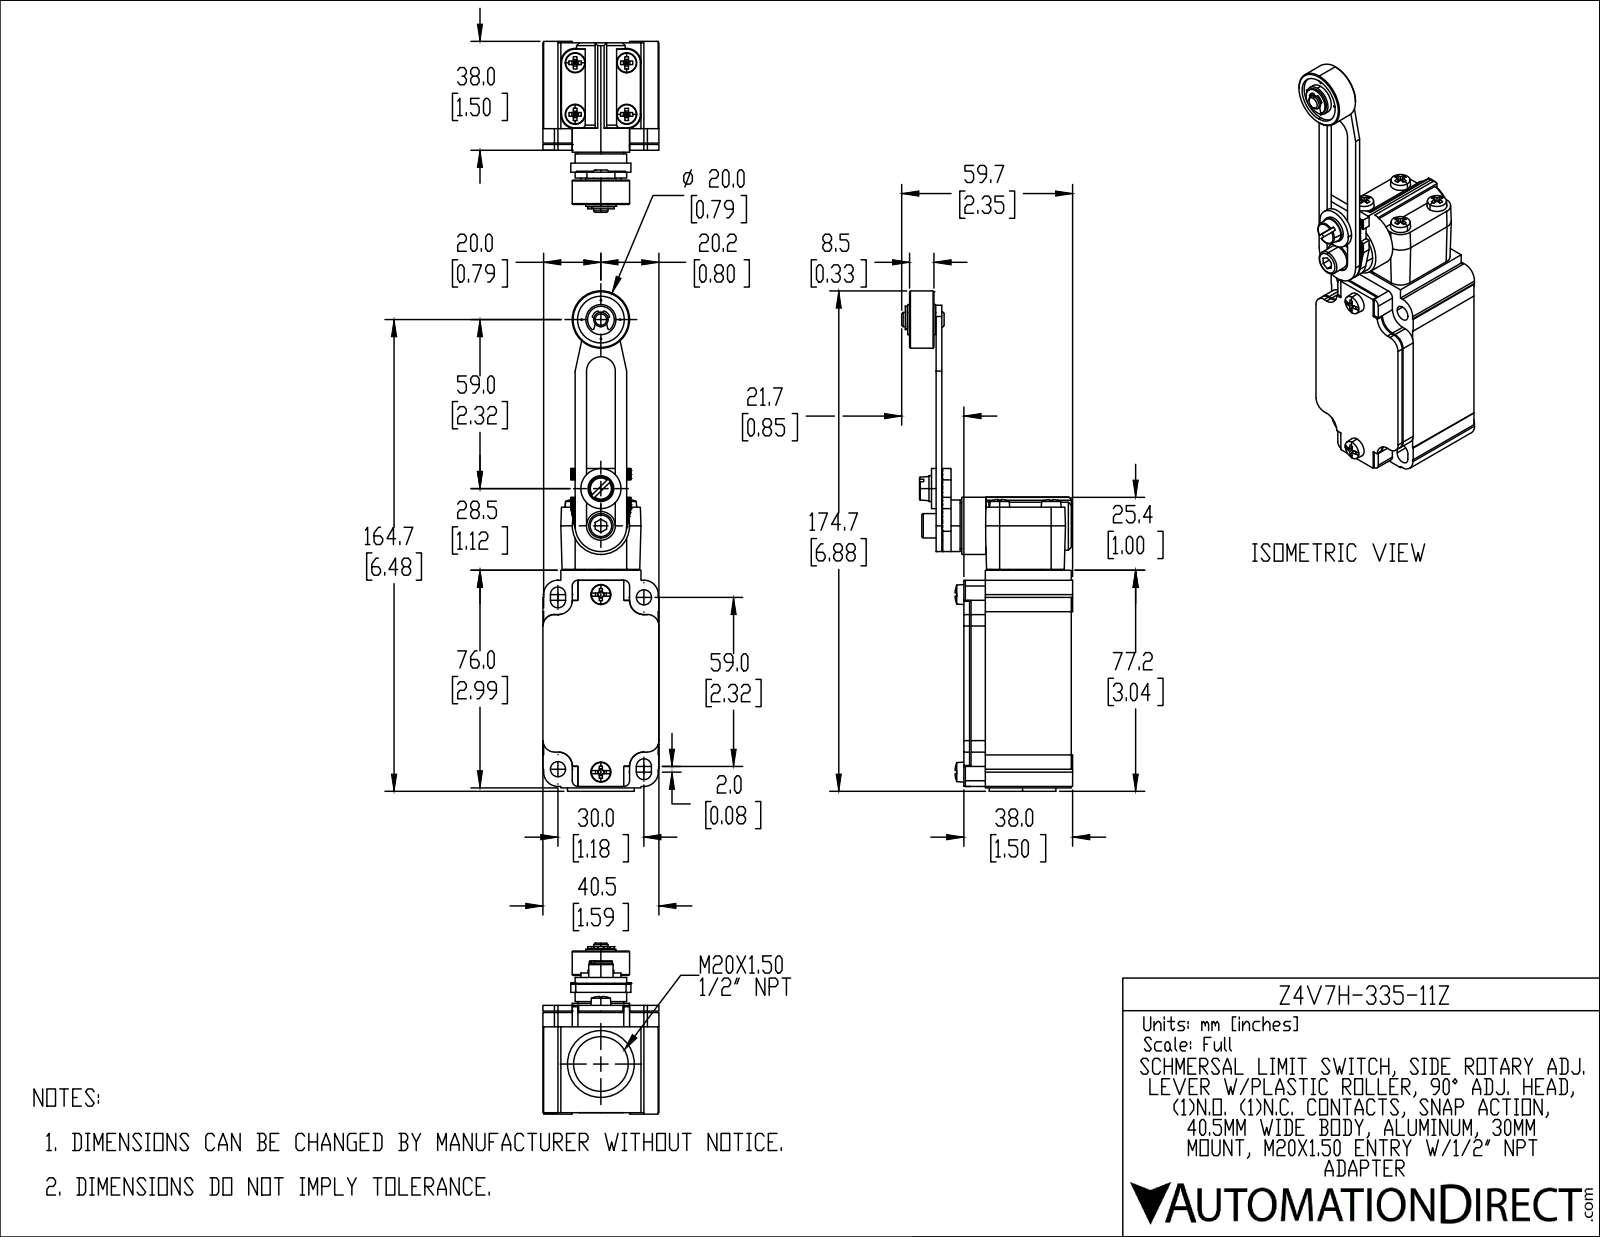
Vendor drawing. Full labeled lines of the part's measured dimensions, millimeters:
Part name (STEP PRODUCT): Z4V7H-335-11Z
STEP written by: SolidWorks 2019 (AUTOMOTIVE_DESIGN)
Units: millimetres
Bodies: 1 solid, 819 faces (592 planar, 160 cylindrical, 67 other)
Overall size (bounding box): 174.7 × 59.7 × 40.5
Volume: 129 400 mm³ · Surface area: 32 060 mm²
Round holes (diameter × count): ⌀0.5 ×4, ⌀5.3 ×2, ⌀16.3 ×1, ⌀16.5 ×1, ⌀19.1 ×1
Round bosses / shafts (diameter × count): ⌀20 ×2, ⌀18 ×2, ⌀4 ×2, ⌀2 ×2, ⌀23.3 ×1, ⌀17 ×1, ⌀16 ×1, ⌀14 ×1
Partial cylindrical surfaces — rounded edges, fillets, slot ends (radius × count): R5 ×13, R0.3 ×12, R4 ×12, R0.3 ×4, R2 ×4, R2.6 ×4, R3.3 ×4, R5 ×4
Main face-to-face distances: 2, 0.5, 35.5, 35, 37.5, 2.5, 9.7, 11.7, 12.2, 47.2
Hole centre spacings: 6.8, 9.6, 13.5, 72.3, 29.2, 65.3, 67.1, 72
